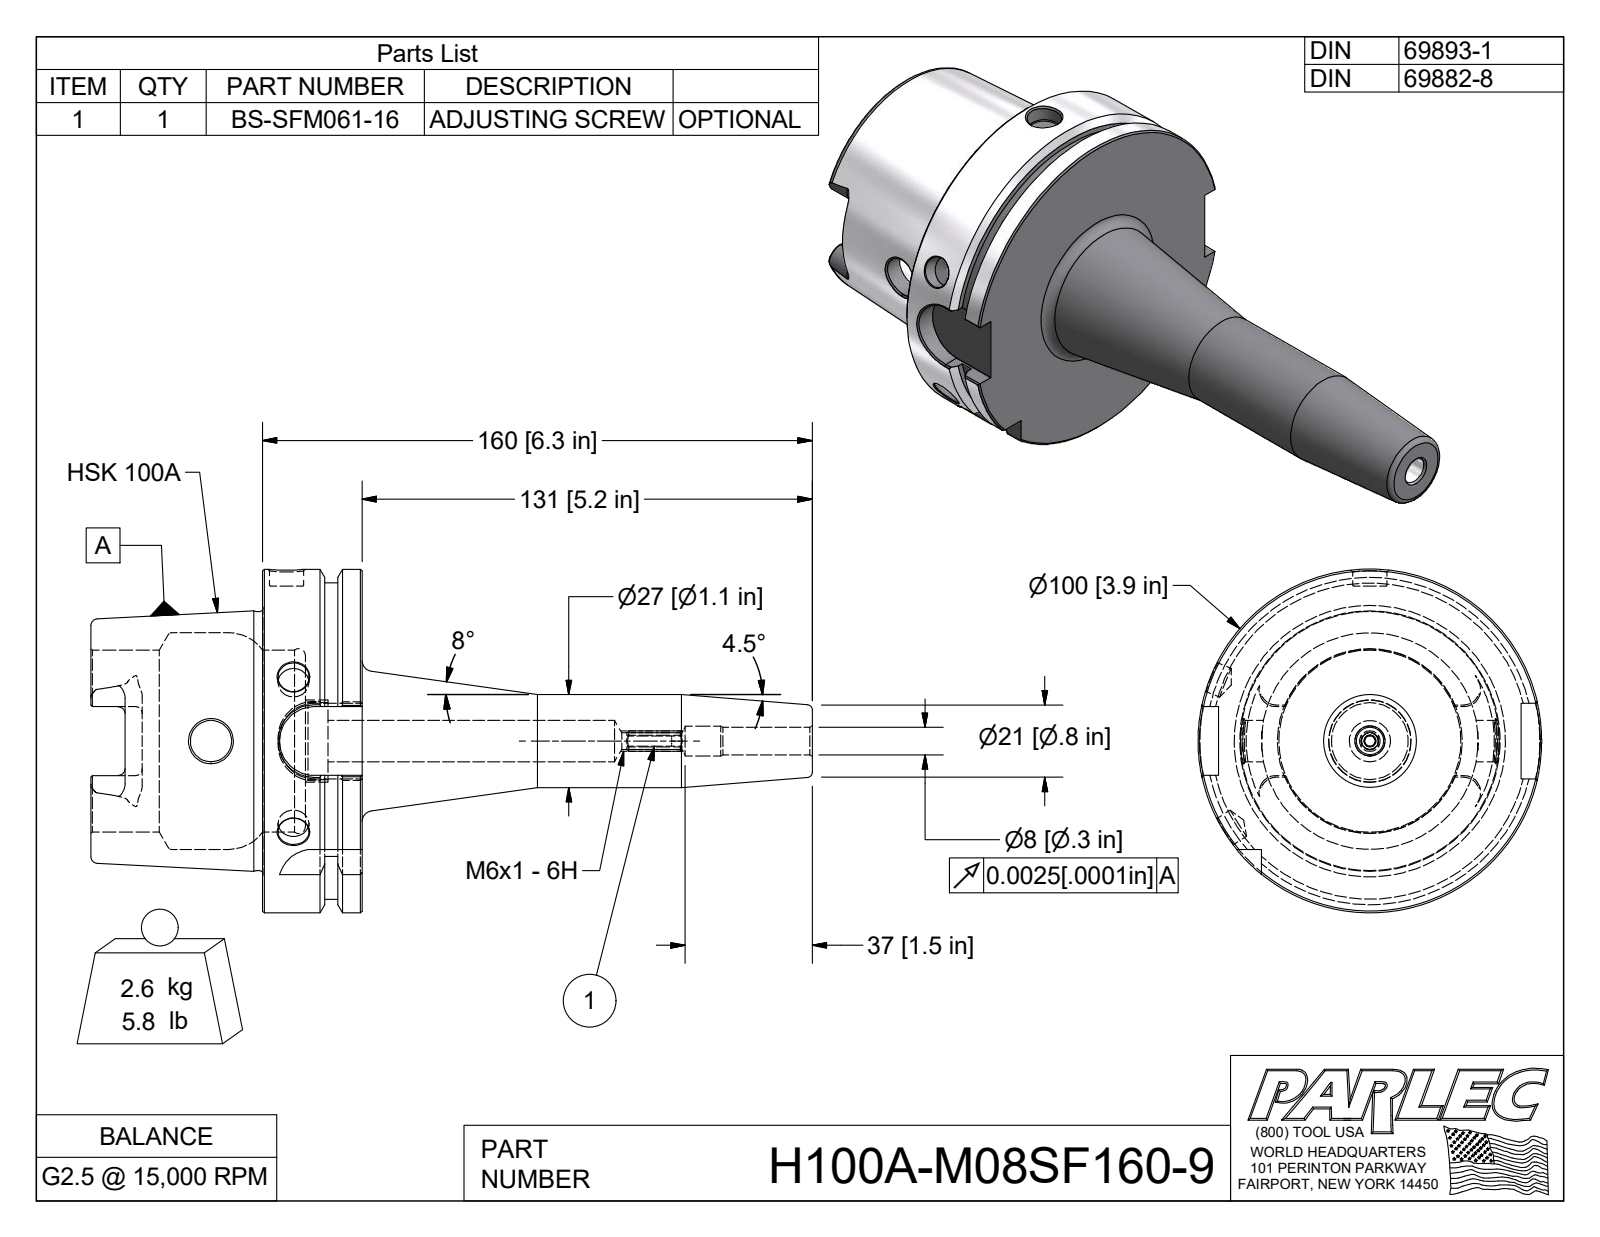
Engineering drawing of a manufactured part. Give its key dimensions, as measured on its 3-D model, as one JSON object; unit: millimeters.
{"part_name": "H100A-M08SF160-9; H100A-M08SF160-9-1; BS-SFM061-16", "step_written_by": "Autodesk Inventor 2009 (AUTOMOTIVE_DESIGN)", "units": "millimeters", "bodies": {"solids": 2, "faces": 153, "planar": 48, "cylindrical": 29, "other": 76}, "overall_size": [210, 100, 100], "volume_mm3": 335100, "surface_area_mm2": 64840, "round_holes": [[8, 1], [8.7, 1], [10, 1], [12, 1], [22.4, 1], [53, 1], [63, 1]], "round_bosses_or_shafts": [[100, 1], [75.4, 1], [27, 1]], "partial_cylinders_radius": [[10, 4], [2, 3], [4.9, 2], [3, 1], [46, 1]], "face_to_face_distances": [29, 12.5, 16.5, 50, 62.5, 79, 68.1, 18.1, 5.6, 10.9]}
